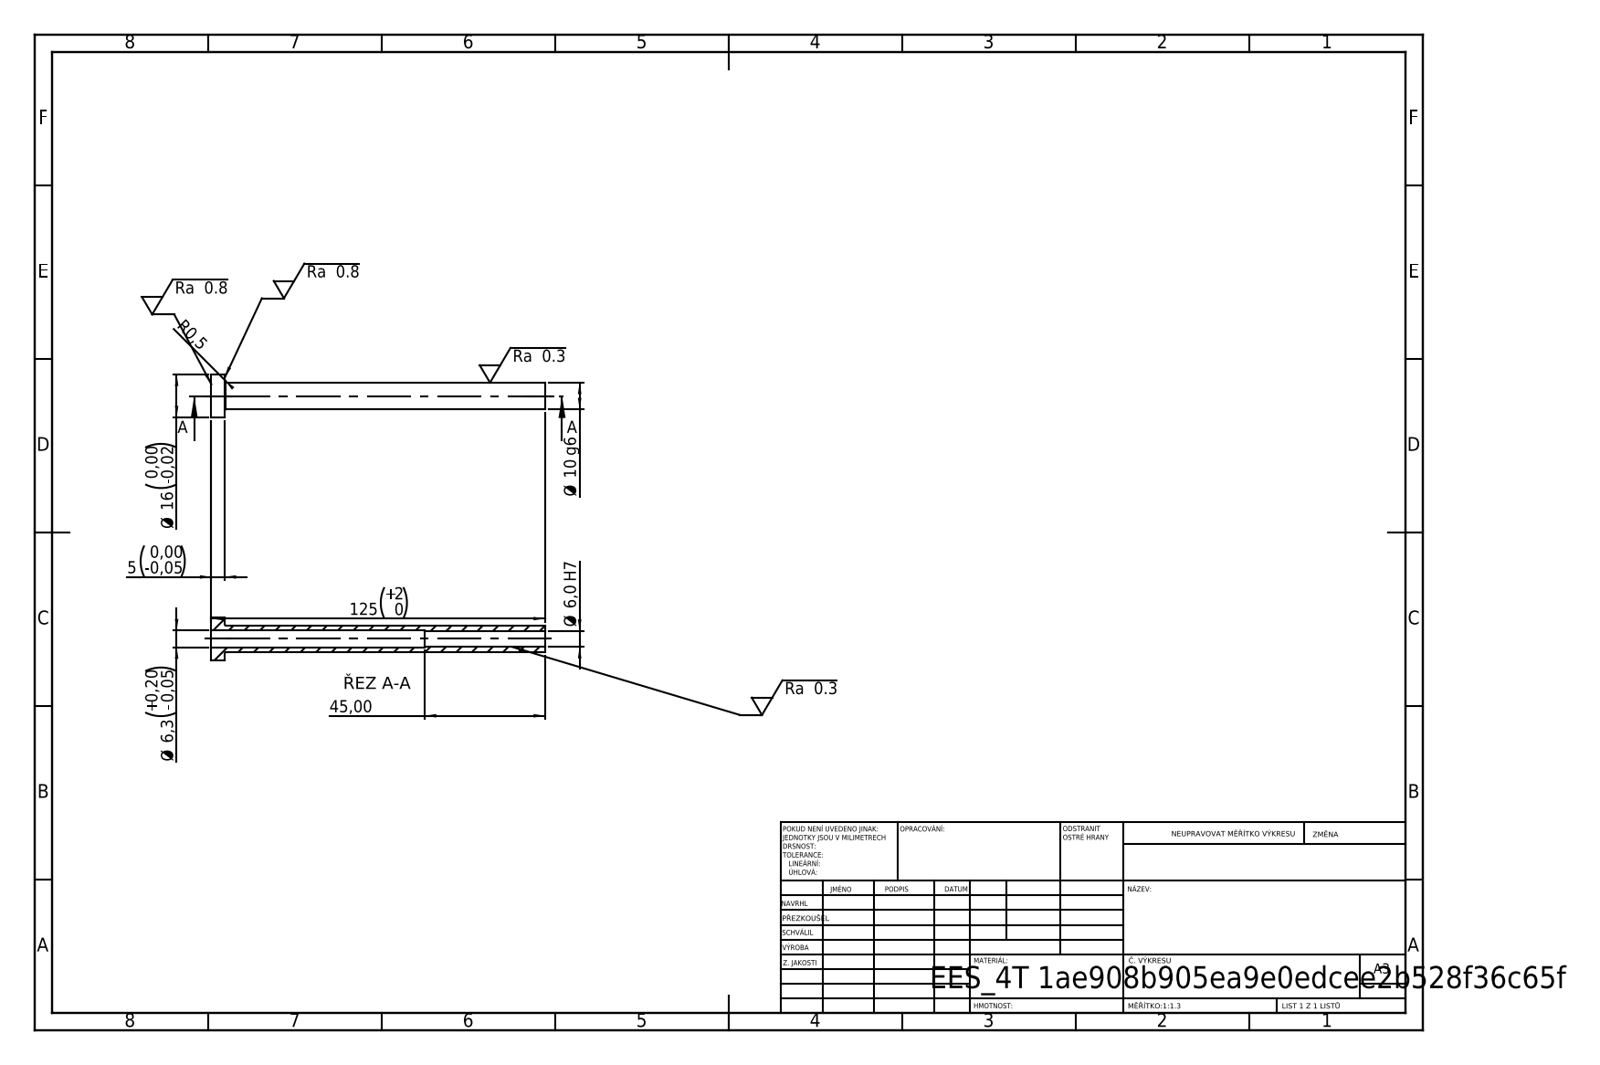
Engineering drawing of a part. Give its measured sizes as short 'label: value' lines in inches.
written by: SolidWorks 2019 (CONFIG_CONTROL_DESIGN)
unit: in
bodies: 1 solid, 14 faces (4 planar, 8 cylindrical, 2 other)
size: 4.921 × 0.63 × 0.63
volume: 0.407 in³; area: 10.53 in²
holes: 1× ⌀0.236, 1× ⌀0.248
bosses: 1× ⌀0.63, 1× ⌀0.394
face distances: 0.197, 4.921, 4.724, 3.15, 2.953, 1.772
